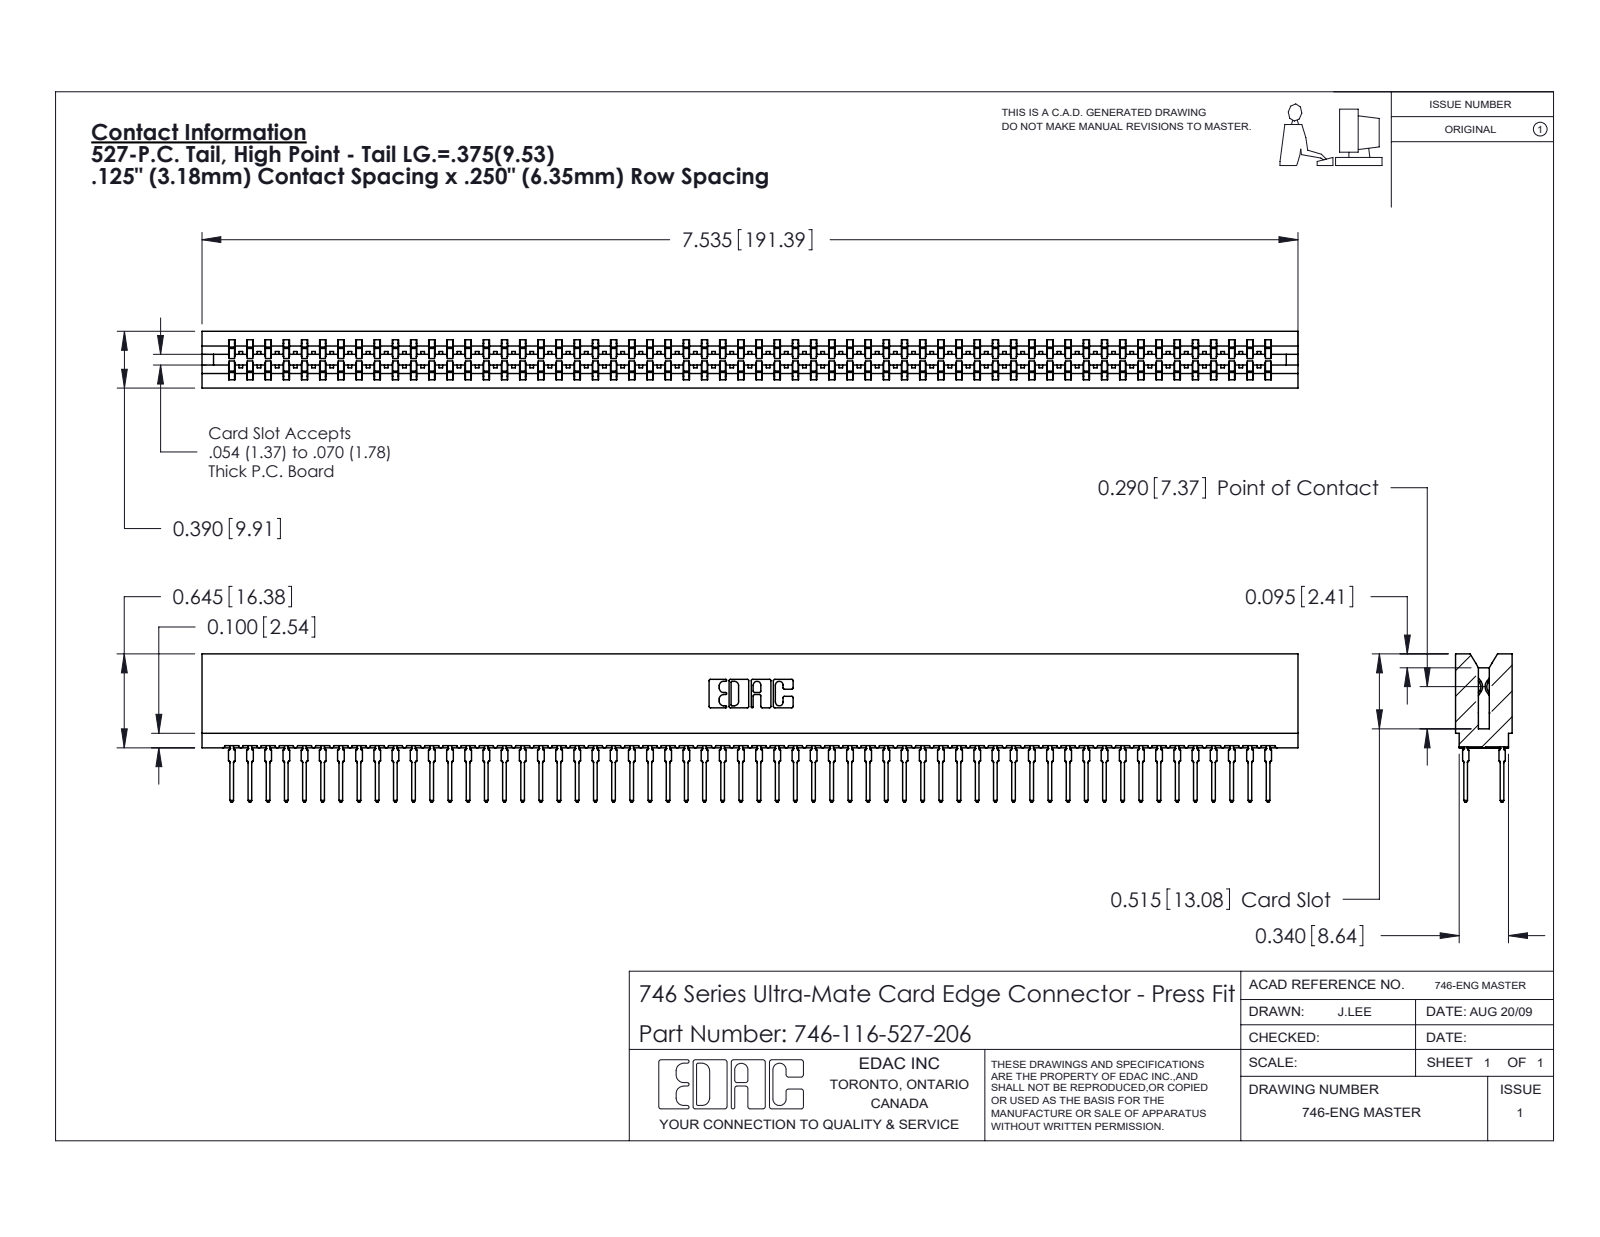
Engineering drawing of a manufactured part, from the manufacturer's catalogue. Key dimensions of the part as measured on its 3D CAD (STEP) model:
Part name (STEP PRODUCT): 746 Part_.515 Slot Depth - 06; 746-292-001_527; 746-116-527-206
STEP written by: SolidWorks 2020 (CONFIG_CONTROL_DESIGN)
Units: inches
Bodies: 117 solids, 10480 faces (5392 planar, 2072 cylindrical, 3016 other)
Overall size (bounding box): 7.535 × 1.019 × 0.39
Volume: 1.255 in³ · Surface area: 53.15 in²
Partial cylindrical surfaces — rounded edges, fillets, slot ends (radius × count): R0.021 ×232, R0.015 ×59, R0.01 ×22, R0.005 ×8, R0.011 ×8, R0.007 ×6, R0.031 ×6, R0.026 ×3
Main face-to-face distances: 0.057, 0.333, 0.39, 0.25, 0.025, 0.307, 0.275, 0.083, 0.174, 0.158
